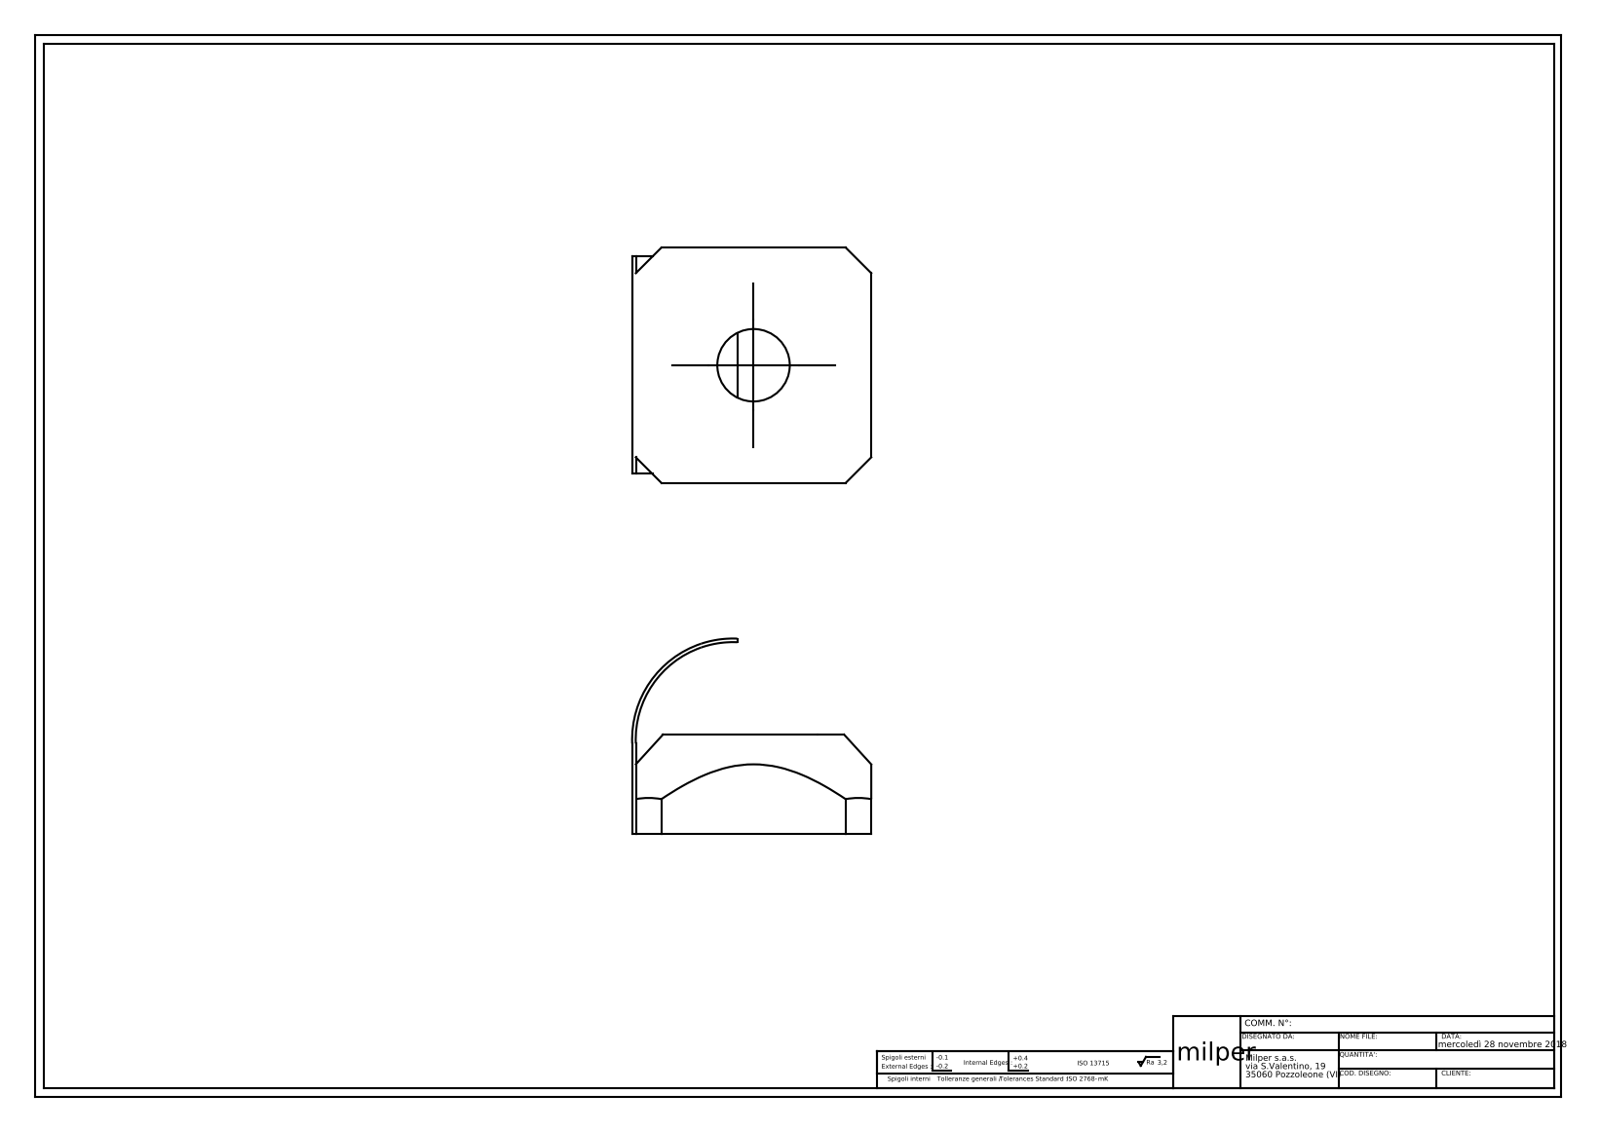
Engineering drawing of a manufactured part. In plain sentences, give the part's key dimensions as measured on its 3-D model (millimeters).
The part is named "dado-M4-molla-3D". Its 3-D file was written by "SolidWorks 2018 (CONFIG_CONTROL_DESIGN)". It is 1 solid with 22 faces: 14 planar, 6 cylindrical and 2 other. Overall it measures 13.21 by 13 by 10.8 millimeters. Its volume is 749 cubic millimeters and its surface area 840 square millimeters. Round holes: 1 of diameter 4. Partial cylindrical surfaces (rounded edges, fillets, slot ends): 2 of radius 2, 1 of radius 5.37, 1 of radius 5.57. The main face-to-face distances are 5.5, 13, 13.2, 16.38, 0.5, 12.5, 12, 5.8, 5.6, 7.4.
